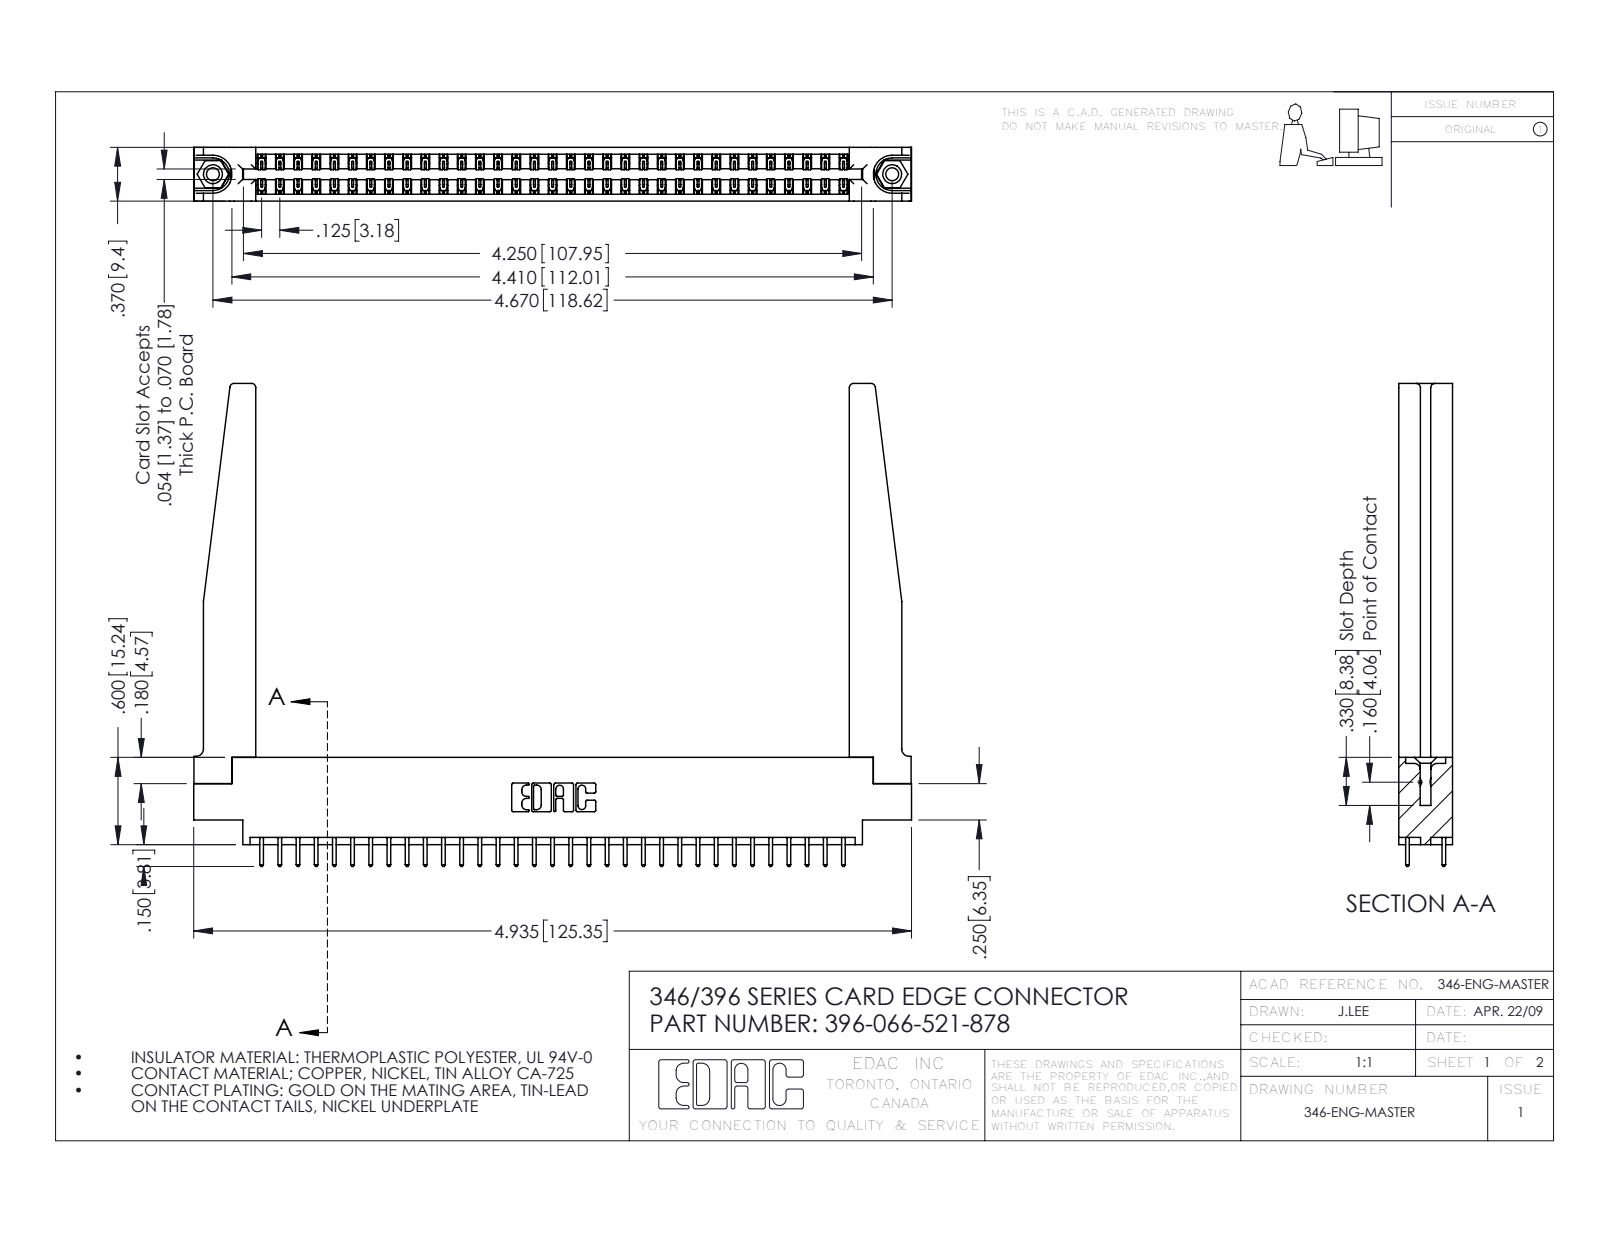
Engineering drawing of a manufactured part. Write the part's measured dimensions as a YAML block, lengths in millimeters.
part_name: "396-066-521-878; 345-292-001_345-293-121; 346-220-078_345-220-078; 346 Part_0.170 Offset - 0.156 Dia-TH (+1 more)"
step_written_by: "SolidWorks 2016 (CONFIG_CONTROL_DESIGN)"
units: millimeters
bodies: {solids: 71, faces: 3792, planar: 2532, cylindrical: 1208, other: 52}
overall_size: [125.3, 84.3, 9.4]
volume: 18880
surface_area: 22850
round_holes:
  - {diameter: 2.3, count: 2}
  - {diameter: 3.2, count: 2}
  - {diameter: 4, count: 2}
  - {diameter: 1.6, count: 1}
round_bosses_or_shafts:
  - {diameter: 3.9, count: 2}
partial_cylinders:
  - {radius: 0.2, count: 99}
  - {radius: 0.3, count: 66}
  - {radius: 0.3, count: 22}
  - {radius: 0.8, count: 8}
  - {radius: 0.2, count: 6}
  - {radius: 0.8, count: 6}
  - {radius: 0.7, count: 3}
  - {radius: 0.4, count: 2}
face_to_face_distances: [9.4, 1.2, 8.2, 1.8, 6.4, 3.8, 3.8, 7.6, 0.6, 7]
hole_center_spacings: [6.2, 113.3, 118.6]
